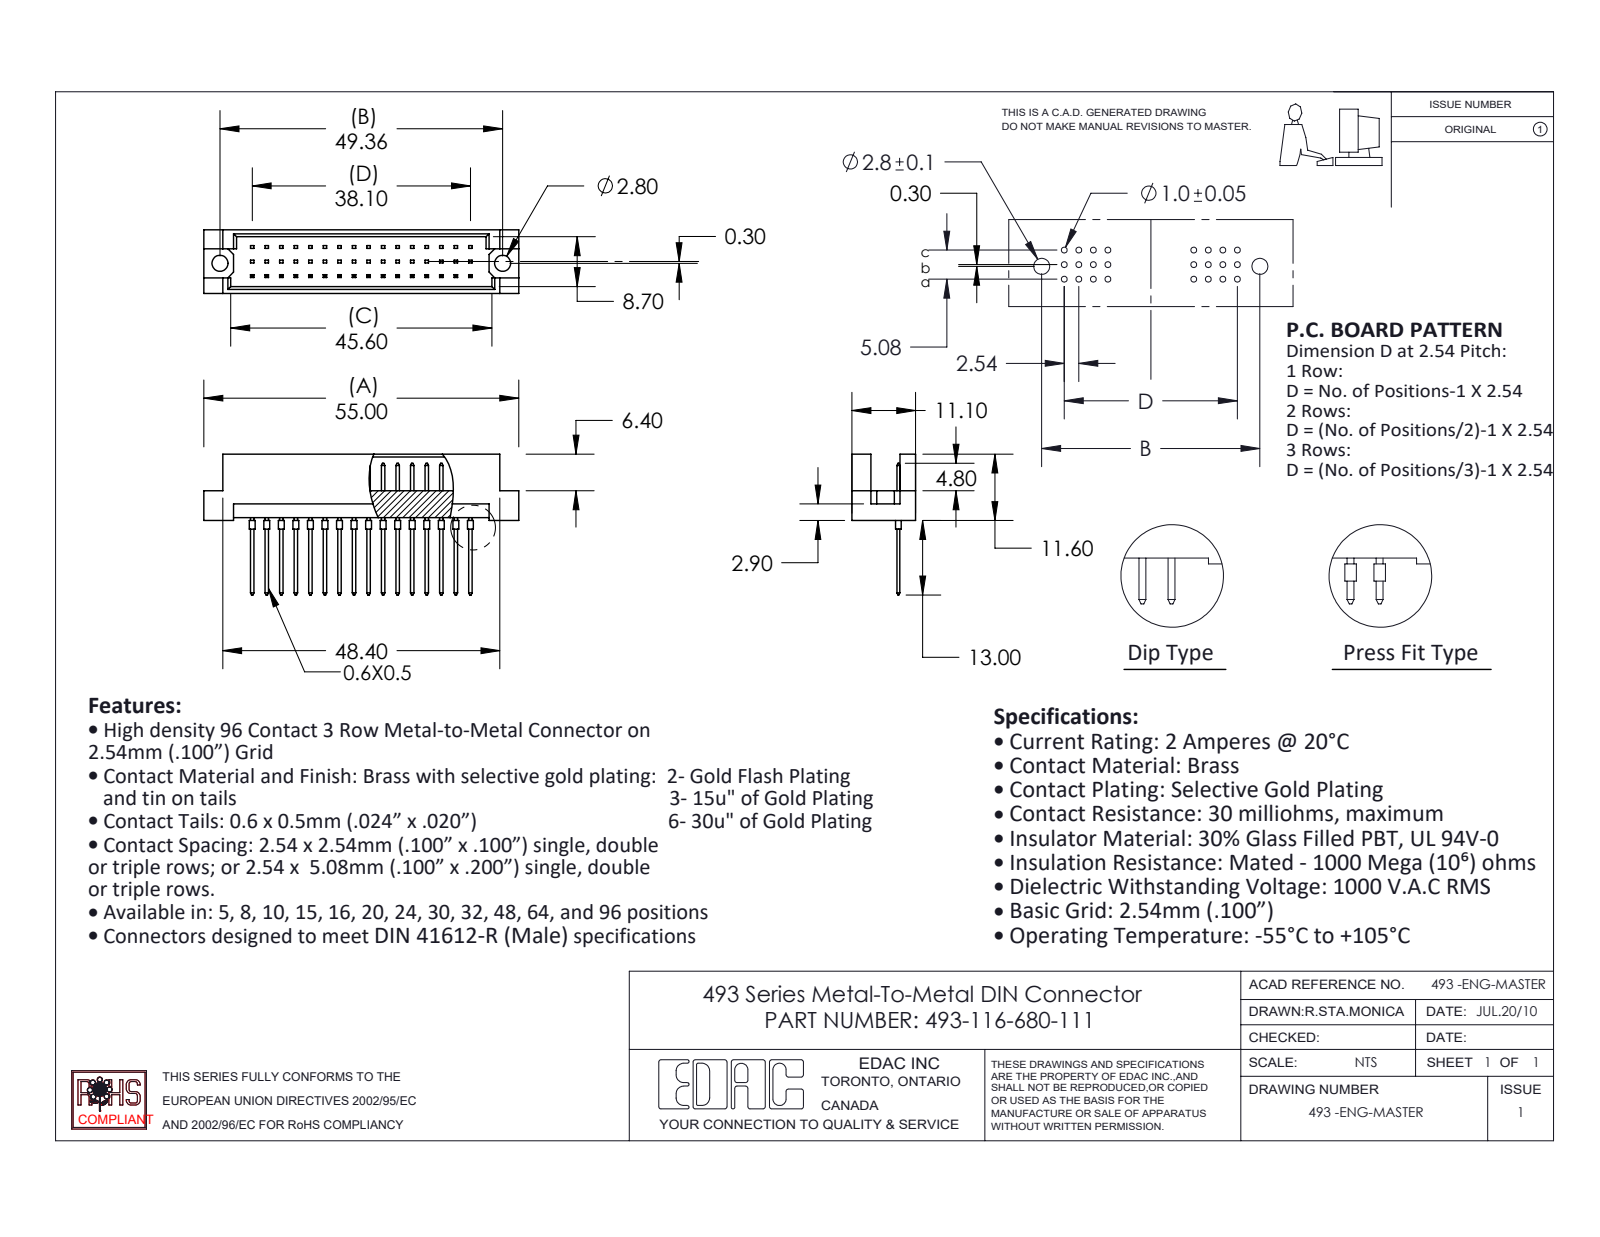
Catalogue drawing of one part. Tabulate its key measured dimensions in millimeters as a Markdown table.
| quantity | value |
| --- | --- |
| part name | 493-116-680-111; 493 Part_48; 493-290_80 |
| STEP written by | SolidWorks 2020 (CONFIG_CONTROL_DESIGN) |
| units | millimeters |
| bodies | 17 solids, 596 faces (560 planar, 36 cylindrical, 0 other) |
| overall size | 55 × 24.6 × 11.1 |
| volume | 3 393 mm³ |
| surface area | 4 598 mm² |
| round holes (diameter × count) | 2.8 × 2 |
| round bosses / shafts (diameter × count) | 1 × 16 |
| main face-to-face distances | 1.2, 9.9, 11.1, 0.5, 8.7, 2.54, 4.7, 5.08, 2.76, 8.34 |
| hole center spacings | 49.36 |
